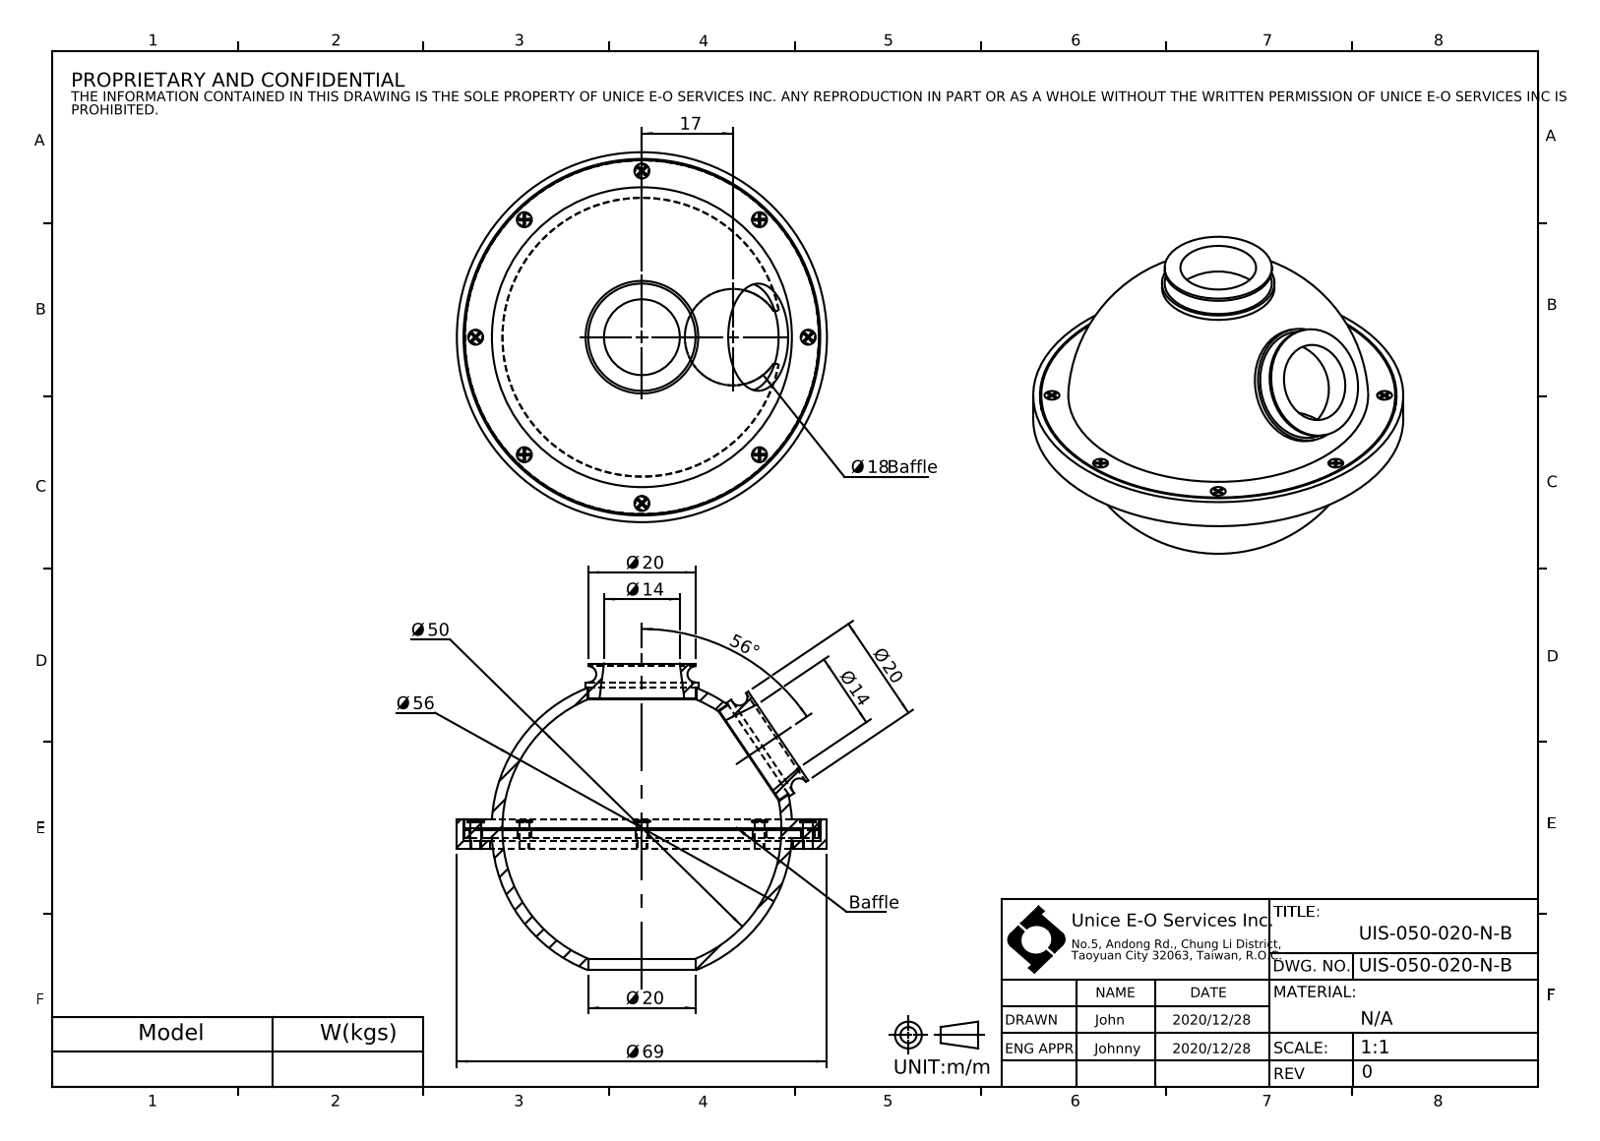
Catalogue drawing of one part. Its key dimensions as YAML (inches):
part_name: "UIS-050-020-N-B"
step_written_by: "SolidWorks 2020 (CONFIG_CONTROL_DESIGN)"
units: inches
bodies: {solids: 0, faces: 72, planar: 28, cylindrical: 24, other: 20}
overall_size: [2.717, 2.717, 2.252]
round_holes:
  - {diameter: 0.787, count: 1}
  - {diameter: 2.224, count: 1}
  - {diameter: 2.618, count: 1}
round_bosses_or_shafts:
  - {diameter: 0.827, count: 2}
  - {diameter: 2.717, count: 1}
  - {diameter: 2.598, count: 1}
  - {diameter: 0.799, count: 1}
  - {diameter: 0.787, count: 1}
face_to_face_distances: [0.059, 0.157, 0.075, 0.083, 0.016, 0.142, 0.217, 0.098, 0.024, 0.134]
